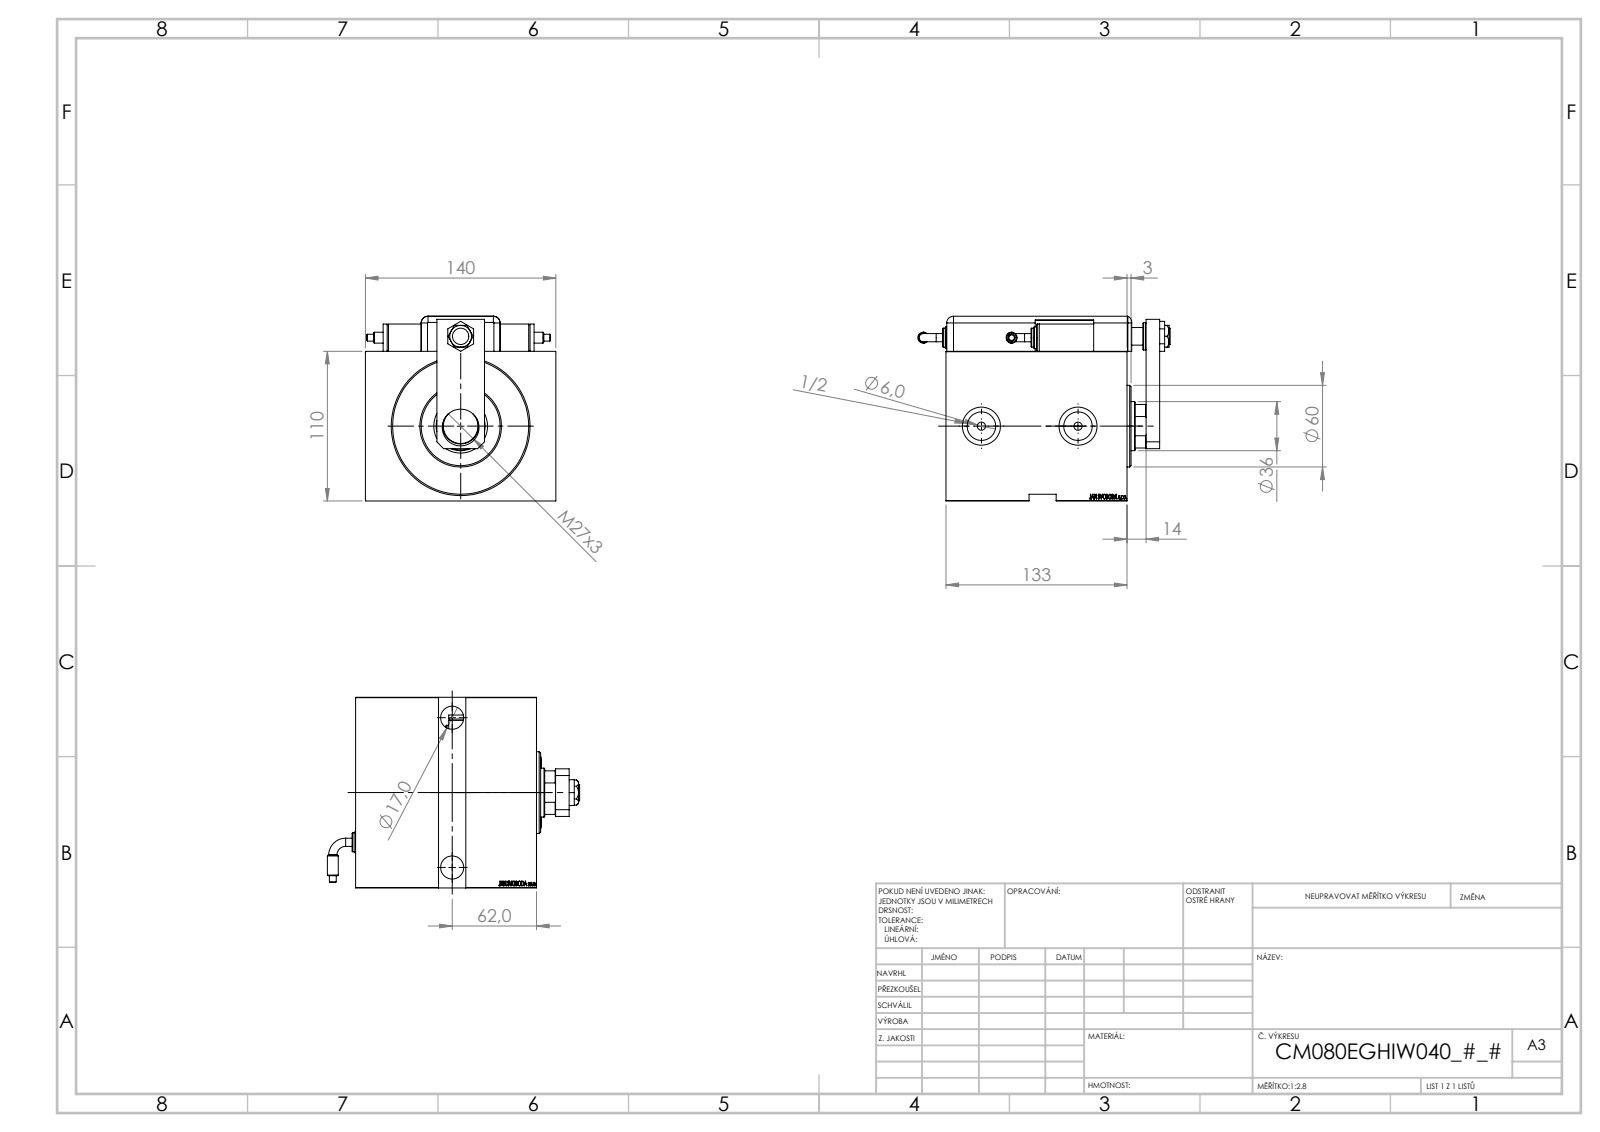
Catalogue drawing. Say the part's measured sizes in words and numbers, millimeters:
The part is named "V450CM_E_VCP; V450CM_E_Body; ZARAZKA_Q; V450CM_VC_B (+7 more)". Its 3-D file was written by "SolidWorks 2019 (CONFIG_CONTROL_DESIGN)". It is 13 solids with 1262 faces: 620 planar, 109 cylindrical and 533 other. Overall it measures 185.46 by 140 by 135.8 millimeters. Its volume is 1 885 000 cubic millimeters and its surface area 258 282 square millimeters. Round holes: 2 of diameter 4, 2 of diameter 6, 2 of diameter 8, 2 of diameter 17, 2 of diameter 20.96, 2 of diameter 25, 2 of diameter 28, 1 of diameter 12, 1 of diameter 13, 1 of diameter 14, 1 of diameter 25.5, 1 of diameter 27. Round bosses or shafts: 3 of diameter 20, 2 of diameter 16, 2 of diameter 14, 2 of diameter 8, 2 of diameter 6, 2 of diameter 5.04, 1 of diameter 60. Partial cylindrical surfaces (rounded edges, fillets, slot ends): 9 of radius 5, 1 of radius 10, 1 of radius 17.5. The main face-to-face distances are 110, 133, 140, 3, 24.5, 108.5, 5, 128, 135.8, 25.8. The hole center spacings are 71.06, 85.15, 1, 20, 66, 67, 71, 110.
